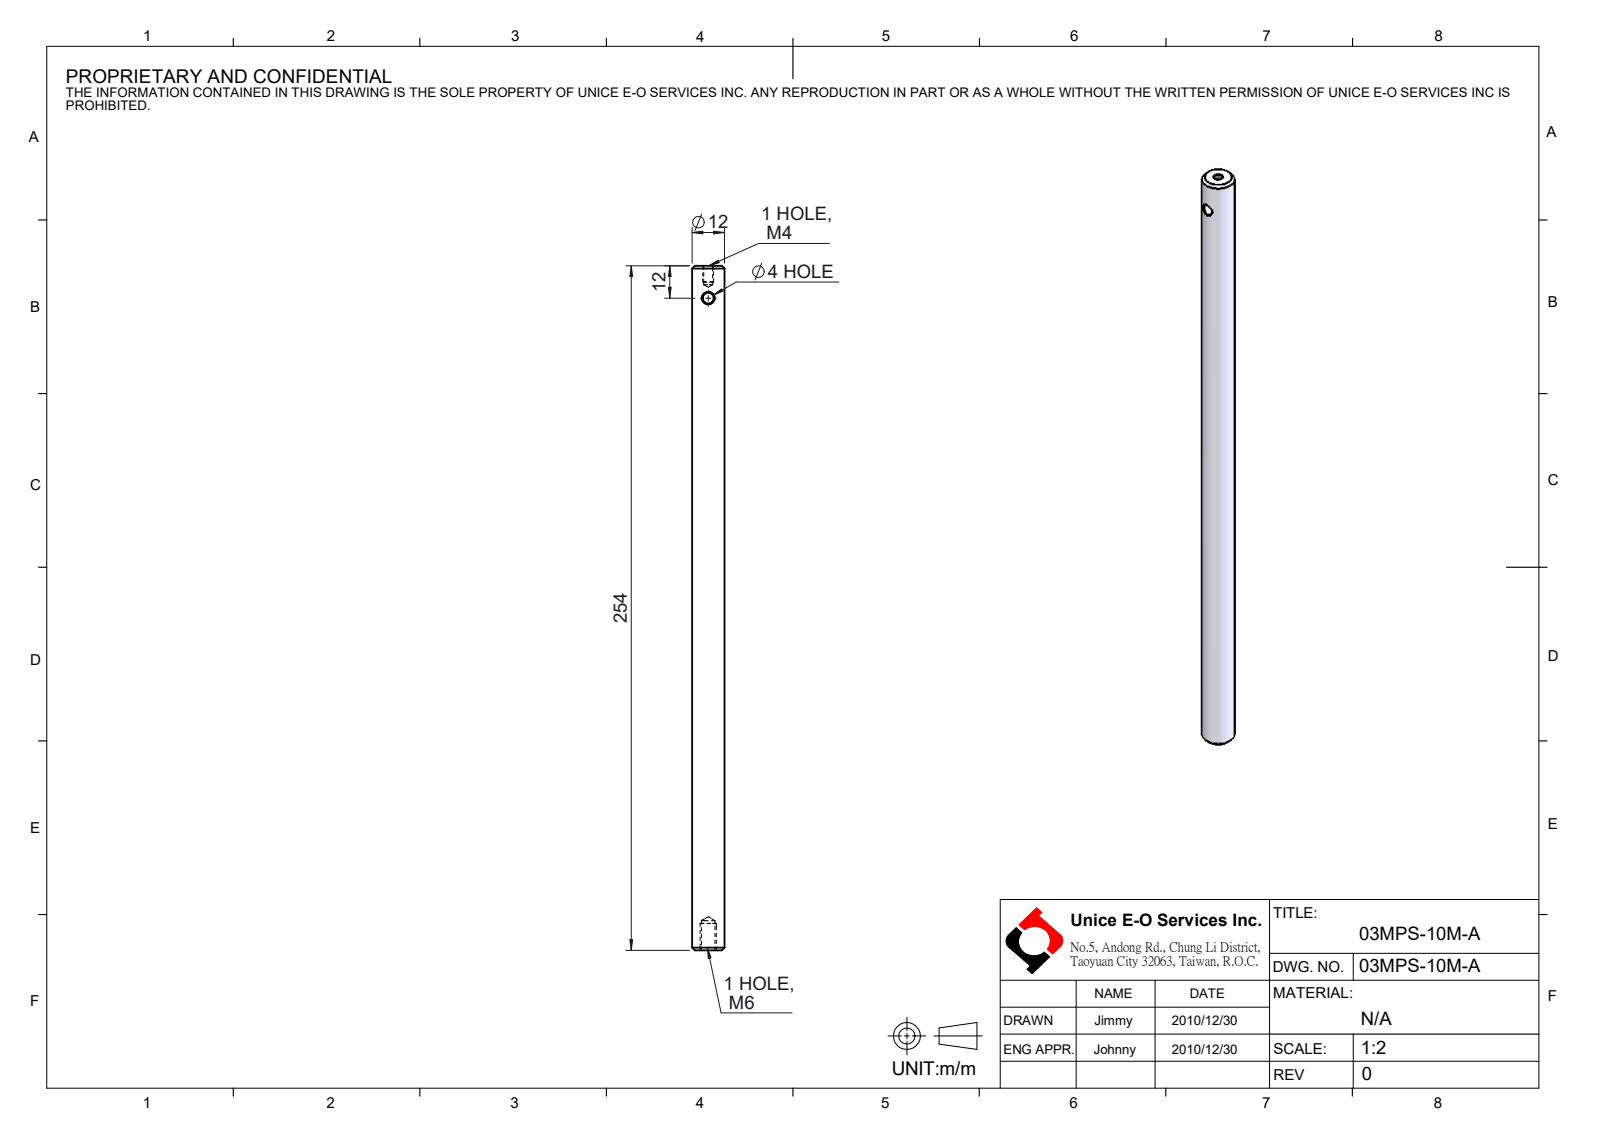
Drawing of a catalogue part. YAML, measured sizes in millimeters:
part_name: "03MPS-10M-A"
step_written_by: "SolidWorks 2016 (CONFIG_CONTROL_DESIGN)"
units: millimeters
bodies: {solids: 1, faces: 22, planar: 2, cylindrical: 8, other: 12}
overall_size: [254, 12, 12]
volume: 28253
surface_area: 10119
round_holes:
  - {diameter: 3.3, count: 1}
  - {diameter: 4, count: 1}
  - {diameter: 5, count: 1}
round_bosses_or_shafts:
  - {diameter: 12, count: 1}
face_to_face_distances: [254]
